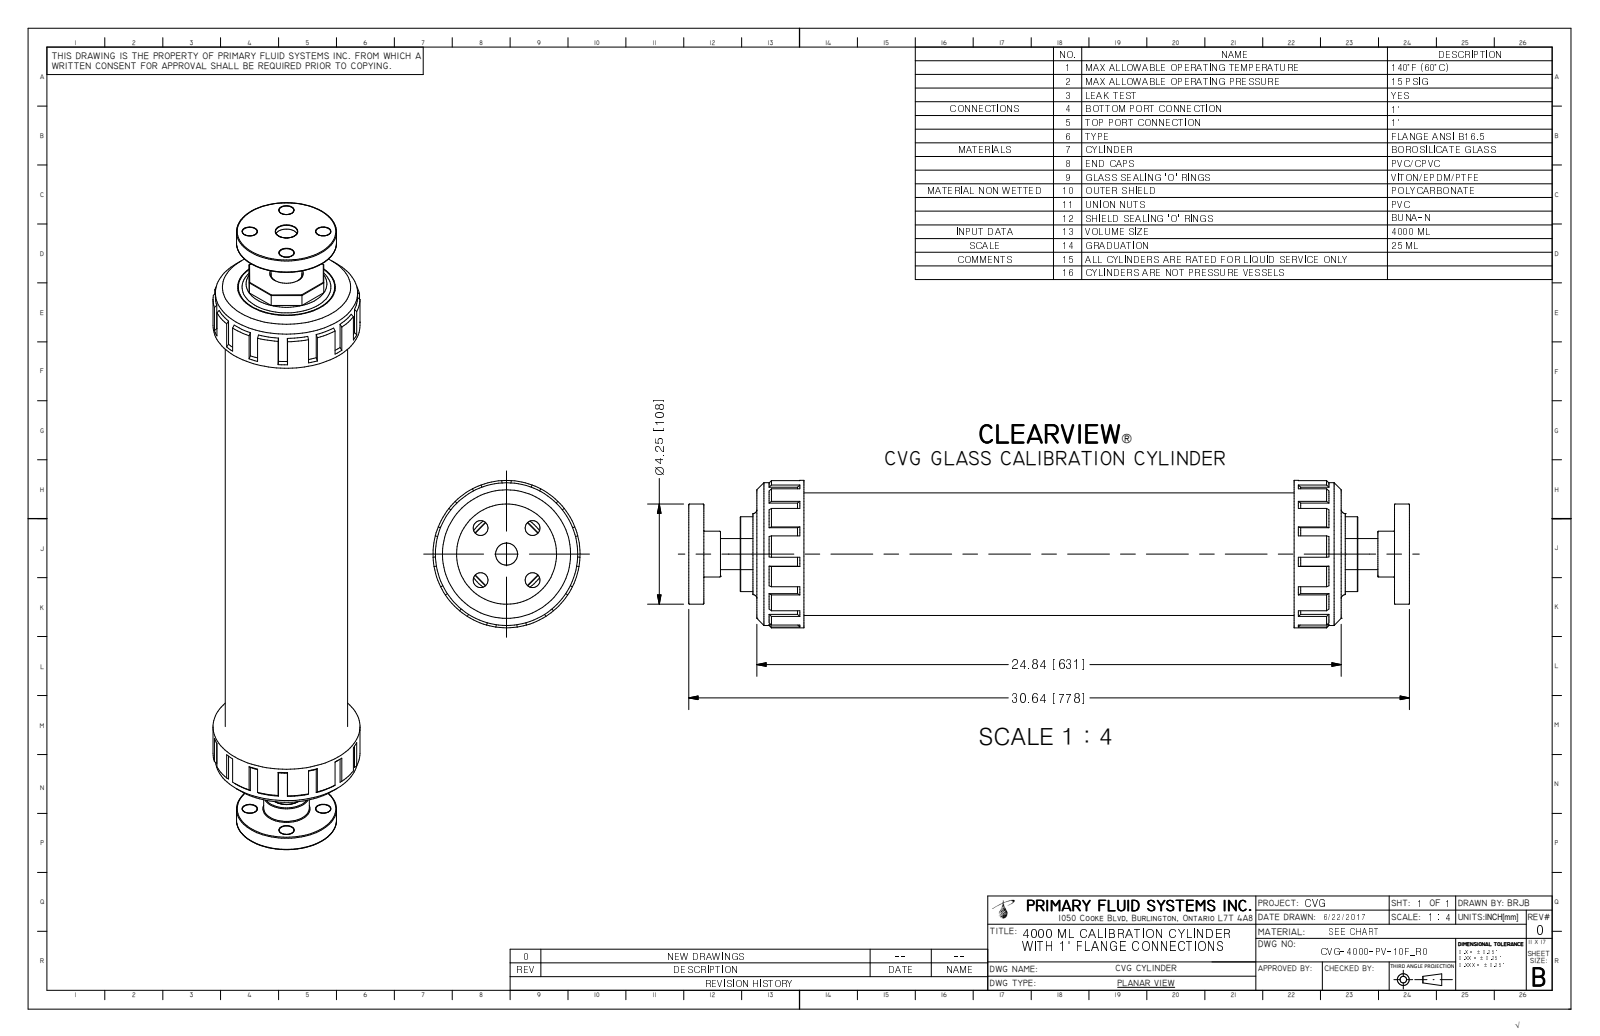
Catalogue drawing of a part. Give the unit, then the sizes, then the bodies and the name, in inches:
Units: inches
Overall size (bounding box): 30.64 × 6.25 × 6.25
Round holes (diameter × count): ⌀0.63 ×4, ⌀0.936 ×1, ⌀0.957 ×1, ⌀4.15 ×1, ⌀5.201 ×1
Round bosses / shafts (diameter × count): ⌀6.25 ×1, ⌀6.05 ×1, ⌀4.933 ×1, ⌀4.25 ×1, ⌀4.1 ×1, ⌀1.941 ×1, ⌀1.315 ×1
Main face-to-face distances: 2, 22.844, 0.635, 30.005, 0.708, 2.708, 23.552, 25.552, 24.844, 2.896
Hole centre spacings: 1.562, 2.209, 3.125
Volume: 591 in³ · Surface area: 708.5 in²
Bodies: 1 solid, 347 faces (100 planar, 51 cylindrical, 196 other)
Part name (STEP PRODUCT): CVG-4000-PV-10F_R0
STEP written by: Autodesk Inventor 2009 (AUTOMOTIVE_DESIGN)
